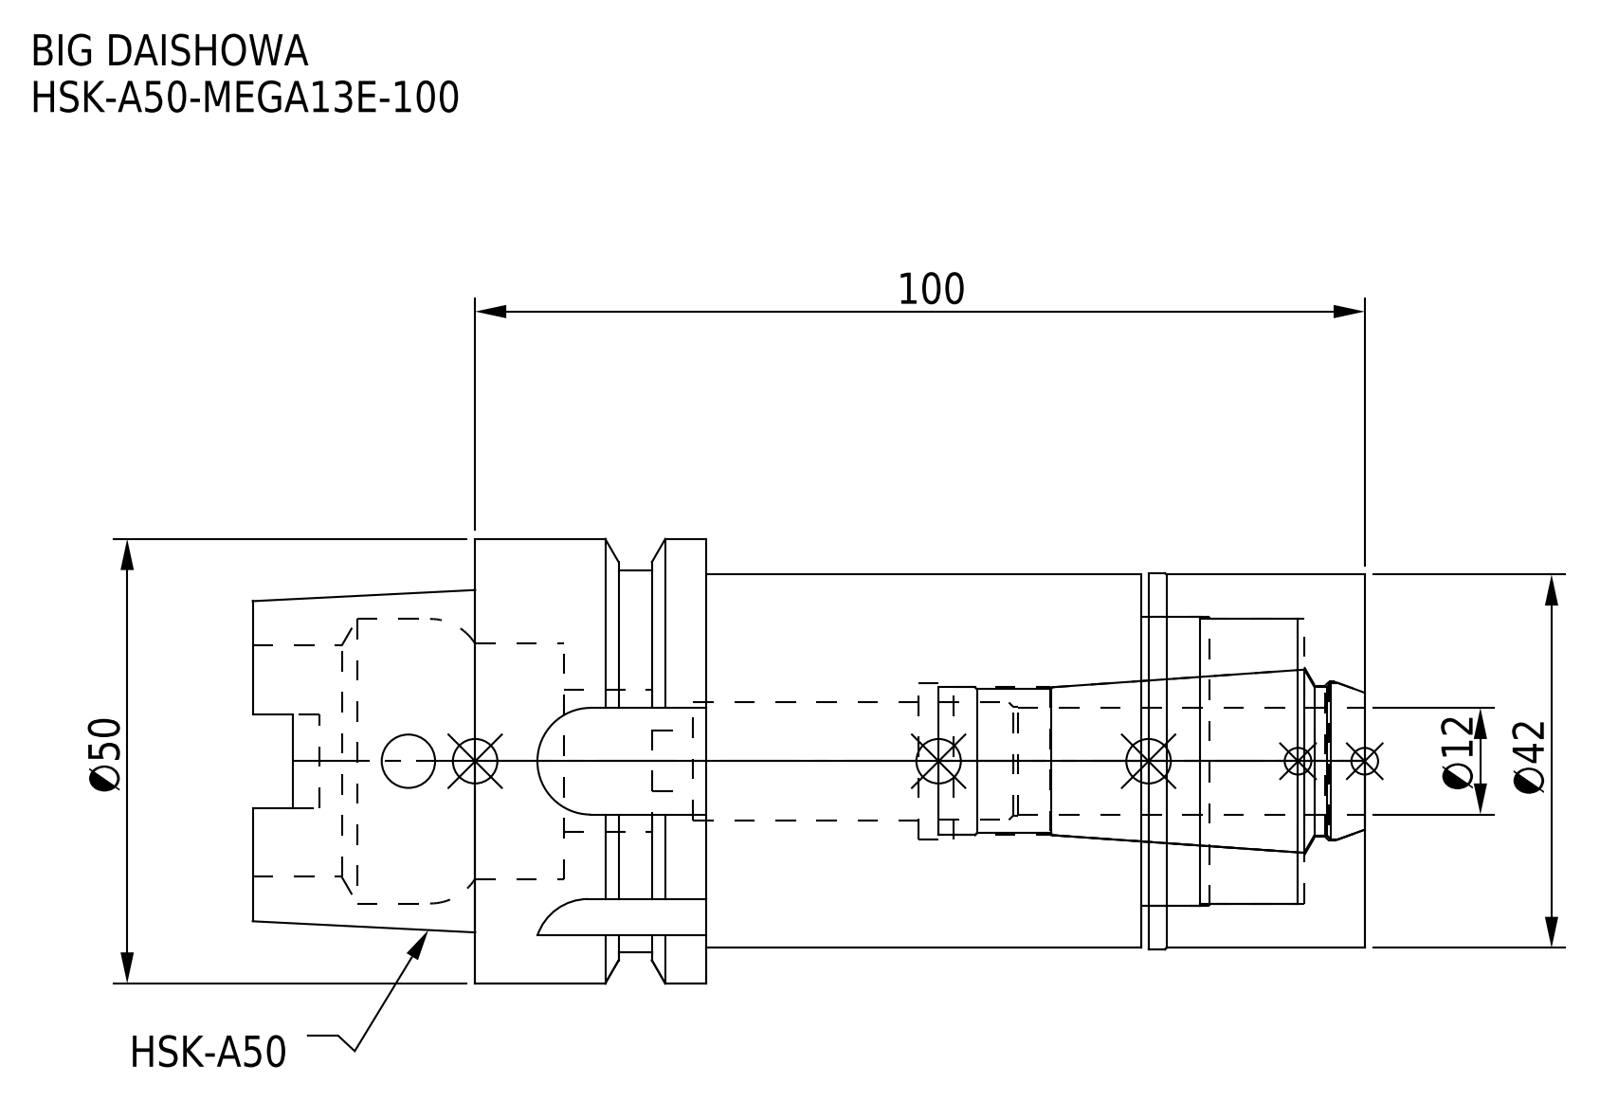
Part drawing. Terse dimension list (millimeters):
name: HSK-A50-MEGA13E-100-120.stp; HSK-A50-MEGA13E-100; DXF_TEMP_ASSY_ASM_4_ASM.stp; HSK-A50-MEGA13E-100_1.stp (+3 more)
written by: SolidWorks 2019 (CONFIG_CONTROL_DESIGN)
unit: mm
bodies: 2 solids, 125 faces (46 planar, 55 cylindrical, 24 other)
size: 125 × 50 × 50
volume: 134 593 mm³; area: 34 450 mm²
holes: 1× ⌀6, 1× ⌀6.8, 1× ⌀13.3, 1× ⌀16, 1× ⌀16.6, 1× ⌀17, 1× ⌀17.53, 1× ⌀17.9, 1× ⌀26, 1× ⌀26.6, 1× ⌀32, 1× ⌀32.5
bosses: 1× ⌀50, 1× ⌀43, 1× ⌀42.3, 1× ⌀42
rounds: 4× R2.38, 4× R6
face distances: 100, 25.1, 24.3, 75.7, 0.8, 74.9, 17.5, 7.5, 93.2, 6.8
